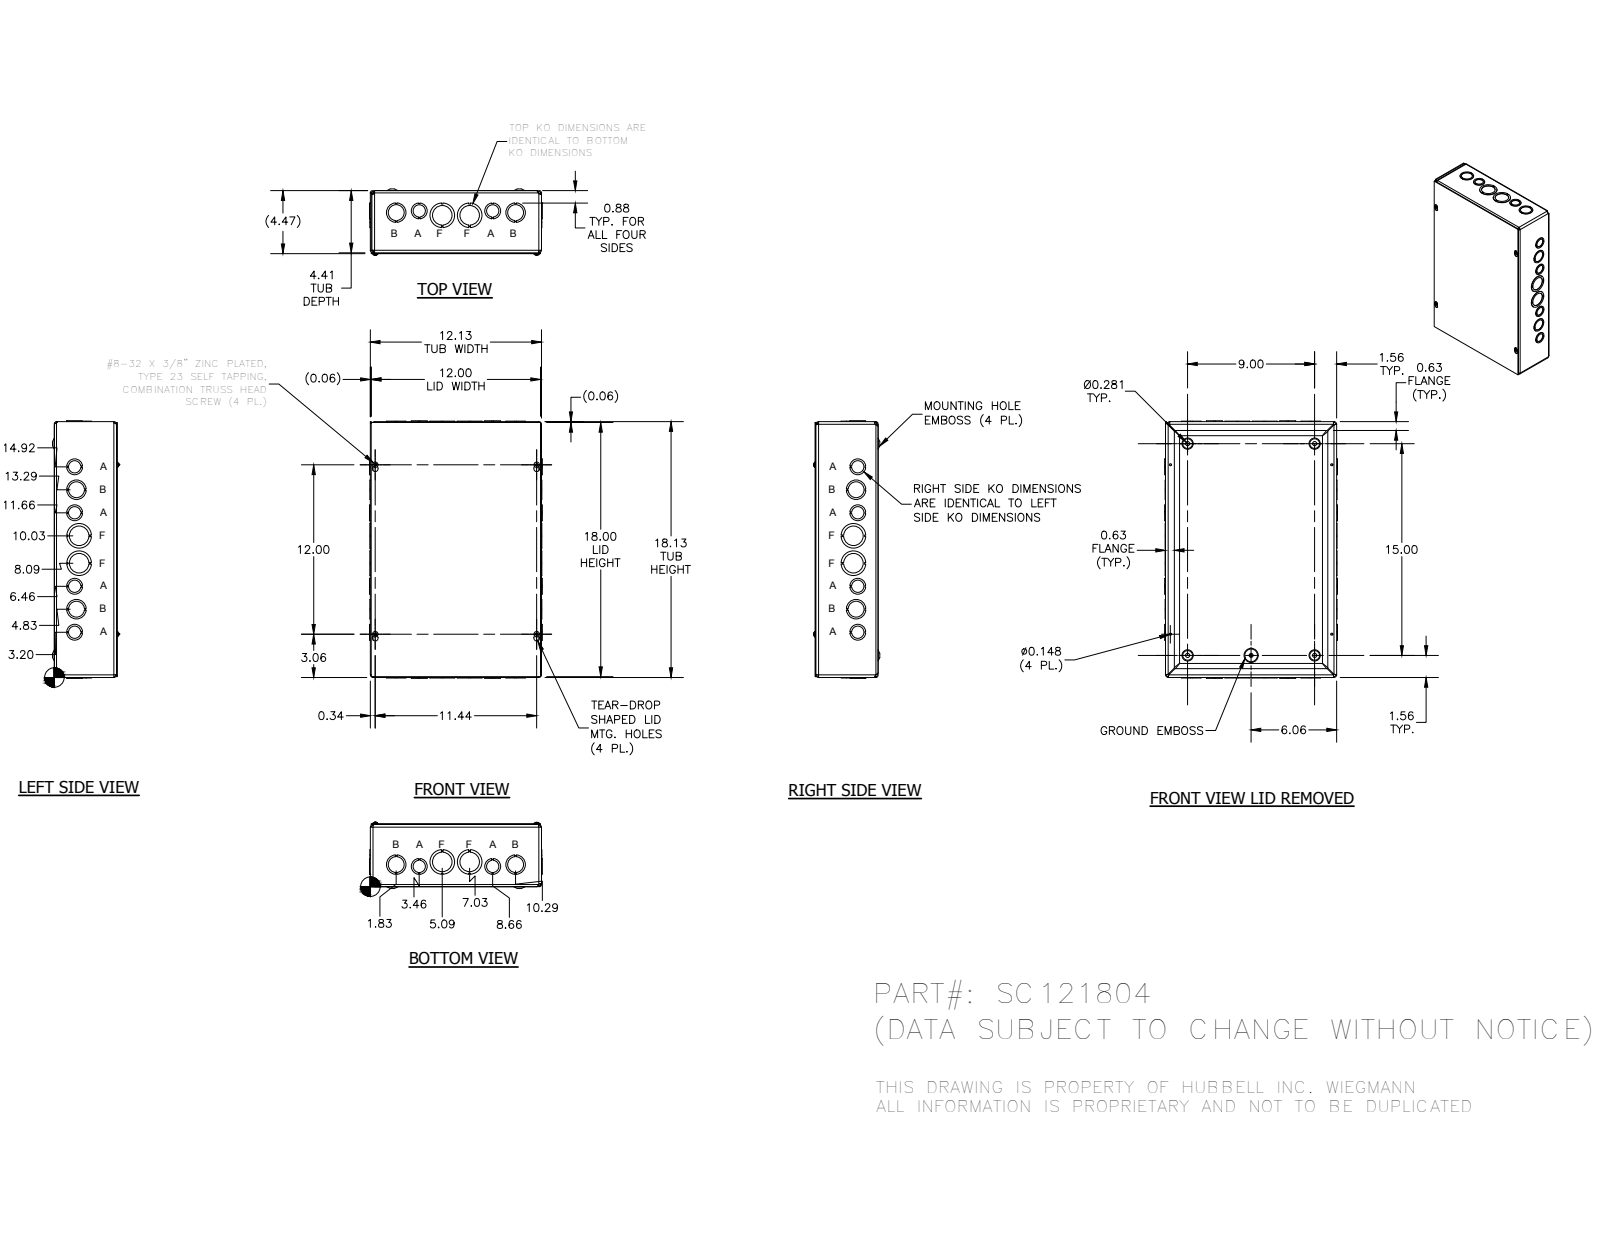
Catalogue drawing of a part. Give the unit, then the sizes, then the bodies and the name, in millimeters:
Units: millimetres
Overall size (bounding box): 463.52 × 311.12 × 119.2
Round holes (diameter × count): ⌀28.57 ×10, ⌀34.92 ×8, ⌀22.22 ×6, ⌀3.76 ×4, ⌀7.62 ×4, ⌀44.45 ×4, ⌀4.19 ×1
Round bosses / shafts (diameter × count): ⌀9.75 ×4, ⌀4.17 ×4, ⌀5.8 ×1
Partial cylindrical surfaces — rounded edges, fillets, slot ends (radius × count): R3.17 ×12, R4.75 ×8, R1.4 ×4, R1.57 ×4, R2.38 ×4, R2.97 ×4, R3.15 ×4, R3.96 ×4
Main face-to-face distances: 1.57, 110.32, 111.89, 1.59, 111.91, 113.48, 1.58, 458.8, 307.98, 306.4
Hole centre spacings: 41.52, 42.15, 49.09, 82.94, 91.03, 132.17, 173.51, 344.29
Bodies: 30 solids, 1142 faces (749 planar, 235 cylindrical, 158 other)
Part name (STEP PRODUCT): SC1218BKP; SC121804WRA; SC1218LID; 34056 (+1 more)
STEP written by: Autodesk Inventor 2014 (AUTOMOTIVE_DESIGN)
